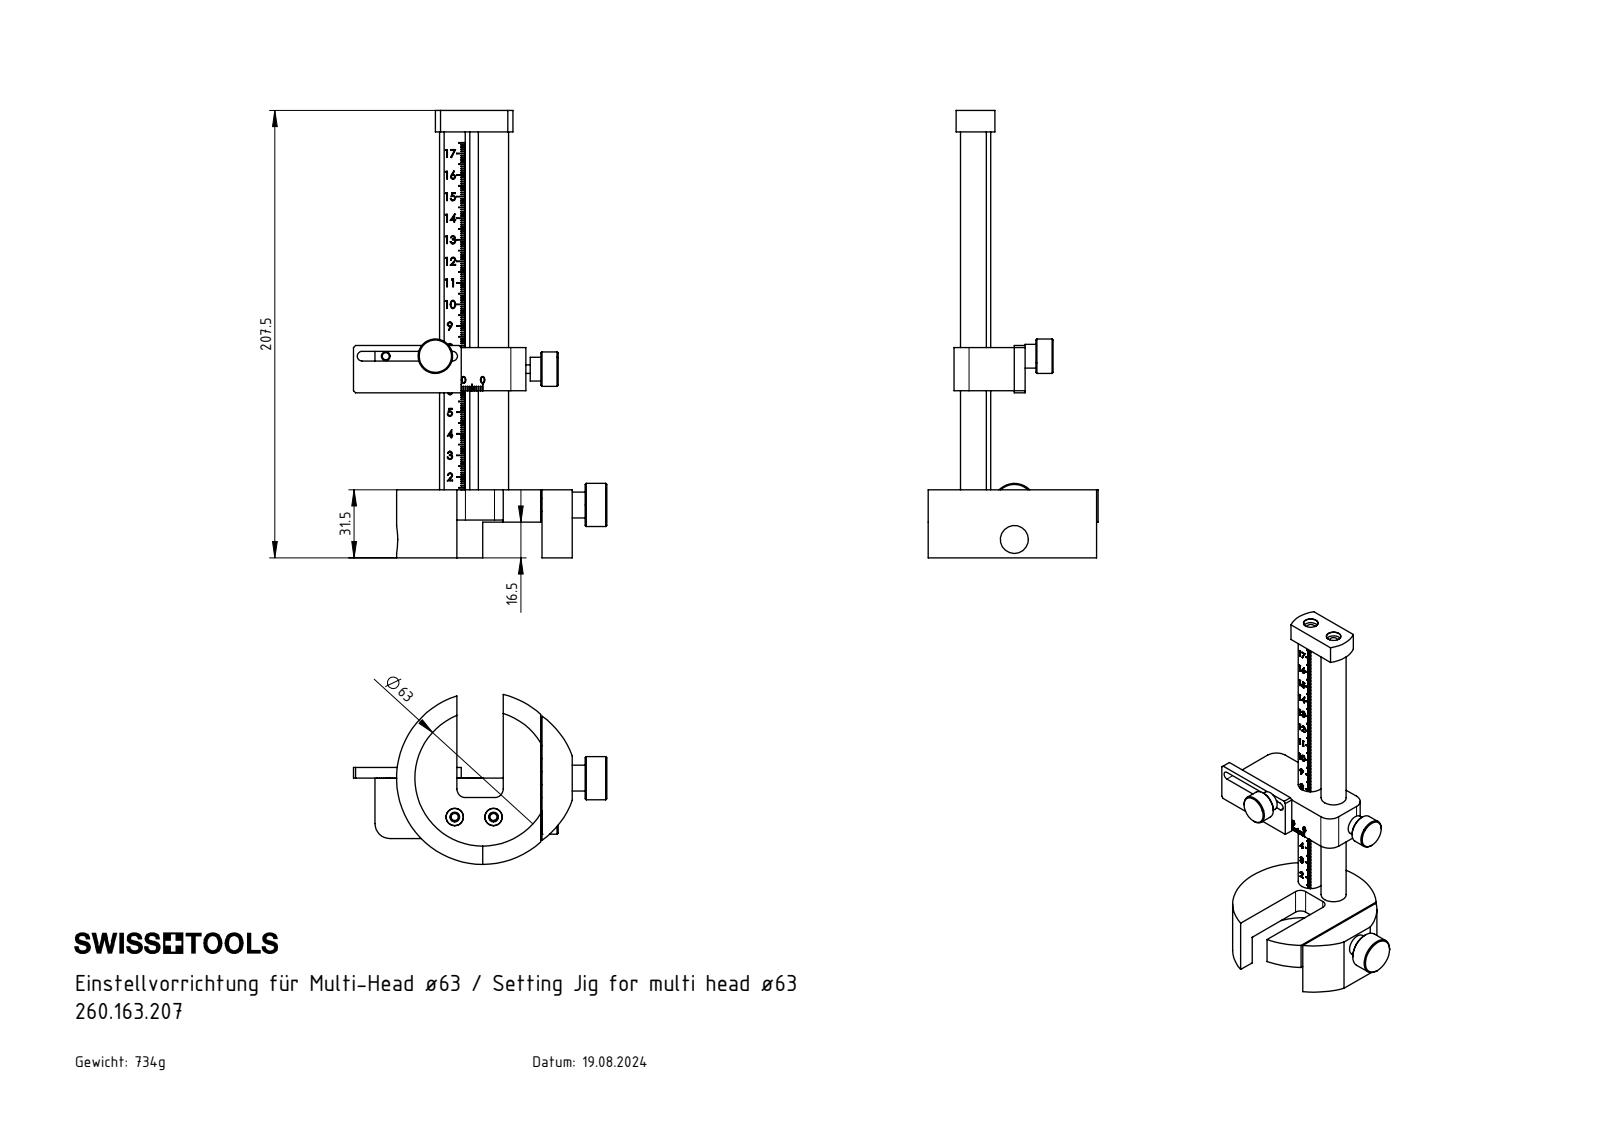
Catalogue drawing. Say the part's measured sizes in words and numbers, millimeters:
The part is named "B20-WCA.K11.105_B; HA6-MH1.BG1.xxx_Fertigbearbeitung; VM6-MH1.090.160_X; VA5-ER7.022.050_A (+8 more)". Its 3-D file was written by "SolidWorks 2017 (CONFIG_CONTROL_DESIGN)". It is 17 solids with 2394 faces: 1648 planar, 321 cylindrical and 425 other. Overall it measures 318.48 by 117.55 by 78.86 millimeters. Its volume is 410 876 cubic millimeters and its surface area 119 929 square millimeters. Round holes: 5 of diameter 3.3, 5 of diameter 4.2, 3 of diameter 6.8, 2 of diameter 3, 2 of diameter 4.5, 2 of diameter 5, 2 of diameter 6, 2 of diameter 8, 2 of diameter 8.5, 2 of diameter 14, 1 of diameter 2, 1 of diameter 2.05. Round bosses or shafts: 3 of diameter 16, 2 of diameter 11, 2 of diameter 4, 1 of diameter 63, 1 of diameter 54.95, 1 of diameter 52, 1 of diameter 47.94, 1 of diameter 20. Partial cylindrical surfaces (rounded edges, fillets, slot ends): 21 of radius 0.14, 20 of radius 0.2, 6 of radius 0.21, 6 of radius 1.4, 6 of radius 6, 5 of radius 0.36, 4 of radius 2.88, 4 of radius 8. The main face-to-face distances are 14, 5, 2.38, 13, 60, 20, 15, 46, 80, 17.5. The hole center spacings are 24, 7.81, 12, 16.73, 18.03, 20, 20.06, 20.52.
